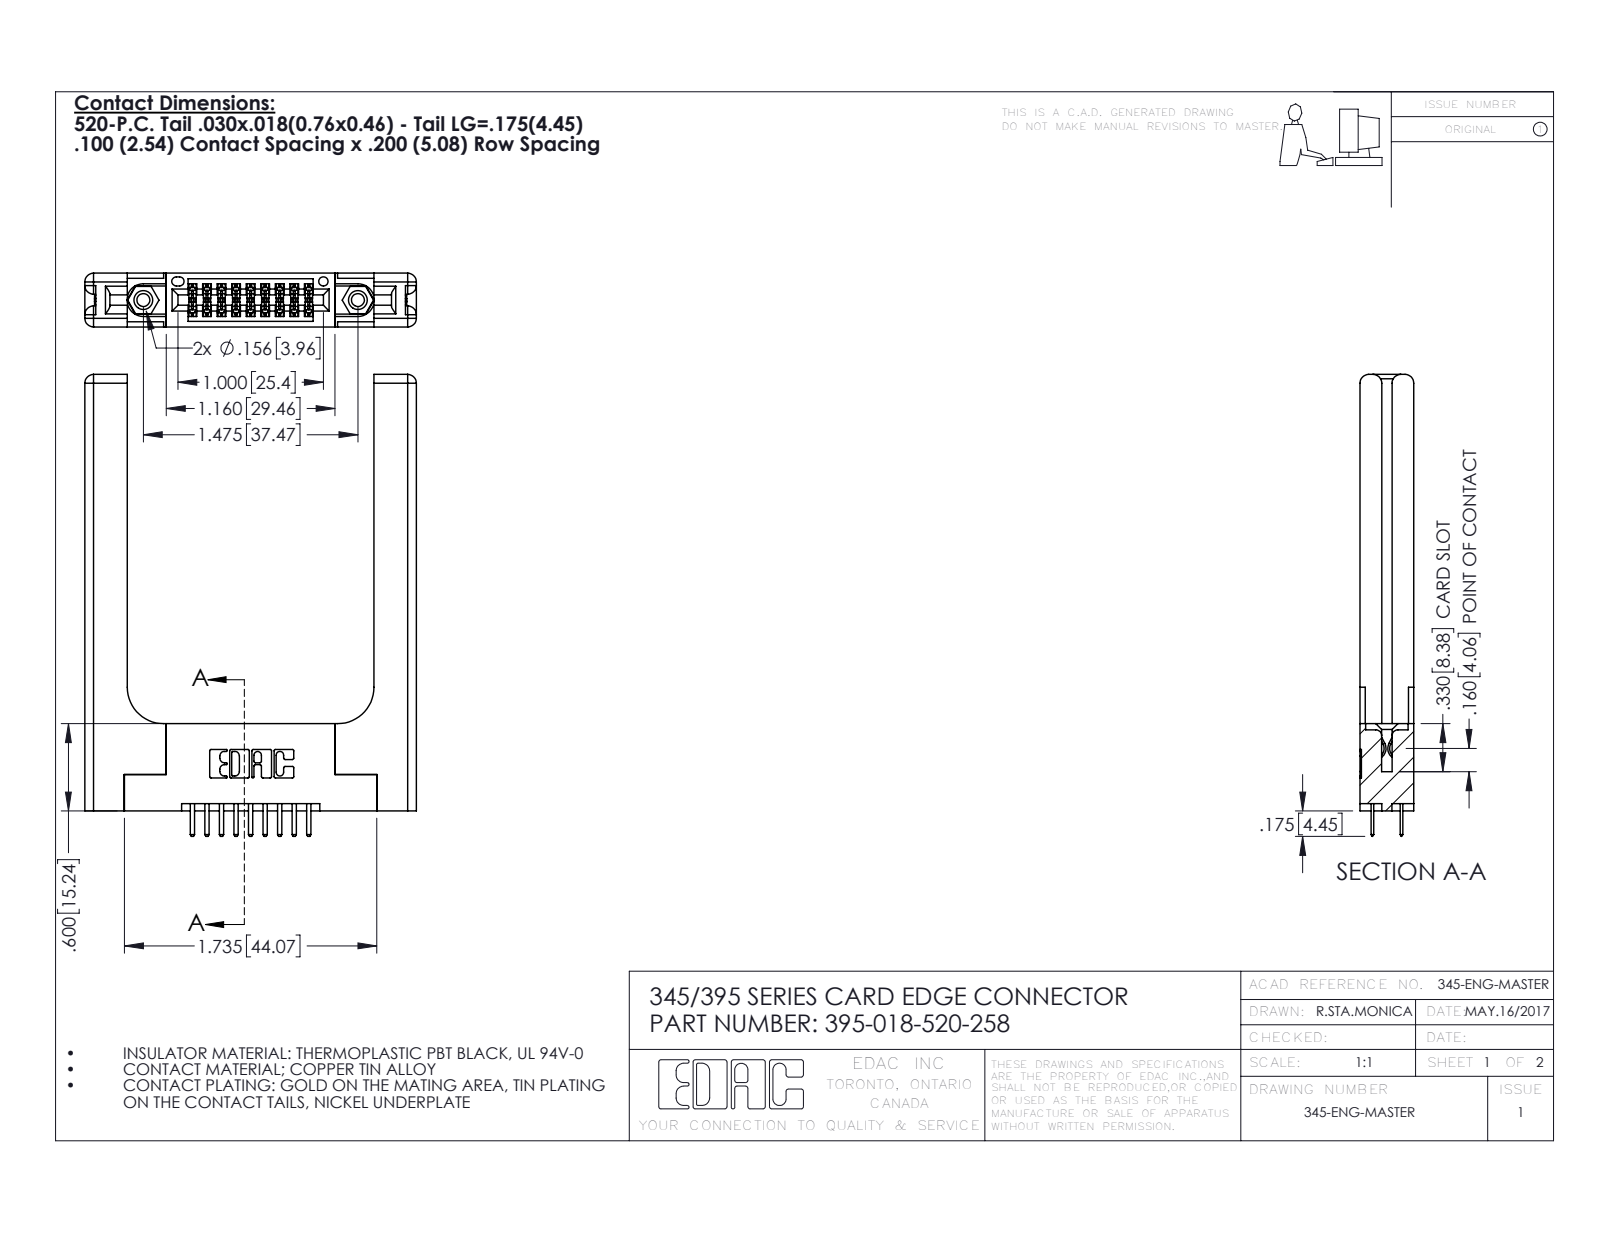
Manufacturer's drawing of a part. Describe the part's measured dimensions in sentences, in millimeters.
The part is named "345-250-001_345-250-001-102; 345 Part_Flush Mounting Lugs - 0.156 Dia-TH; 395-018-520-258; 345-220-058_345-220-058 (+1 more)". Its 3-D file was written by "SolidWorks 2016 (CONFIG_CONTROL_DESIGN)". It is 23 solids with 1354 faces: 858 planar, 436 cylindrical and 60 other. Overall it measures 80.6 by 57.9 by 9.4 millimeters. Its volume is 13 800 cubic millimeters and its surface area 12 250 square millimeters. Round holes: 2 of diameter 2.3, 2 of diameter 3.2, 2 of diameter 4, 1 of diameter 1.6. Round bosses or shafts: 2 of diameter 3.9. Partial cylindrical surfaces (rounded edges, fillets, slot ends): 27 of radius 0.2, 22 of radius 0.3, 22 of radius 0.3, 16 of radius 1.5, 6 of radius 0.2, 6 of radius 0.8, 3 of radius 0.7, 2 of radius 0.4. The main face-to-face distances are 9.4, 3.8, 5.6, 1.8, 2, 7.6, 3.8, 5.1, 43.1, 1.8. The hole center spacings are 6.9, 31.6, 37.5.
